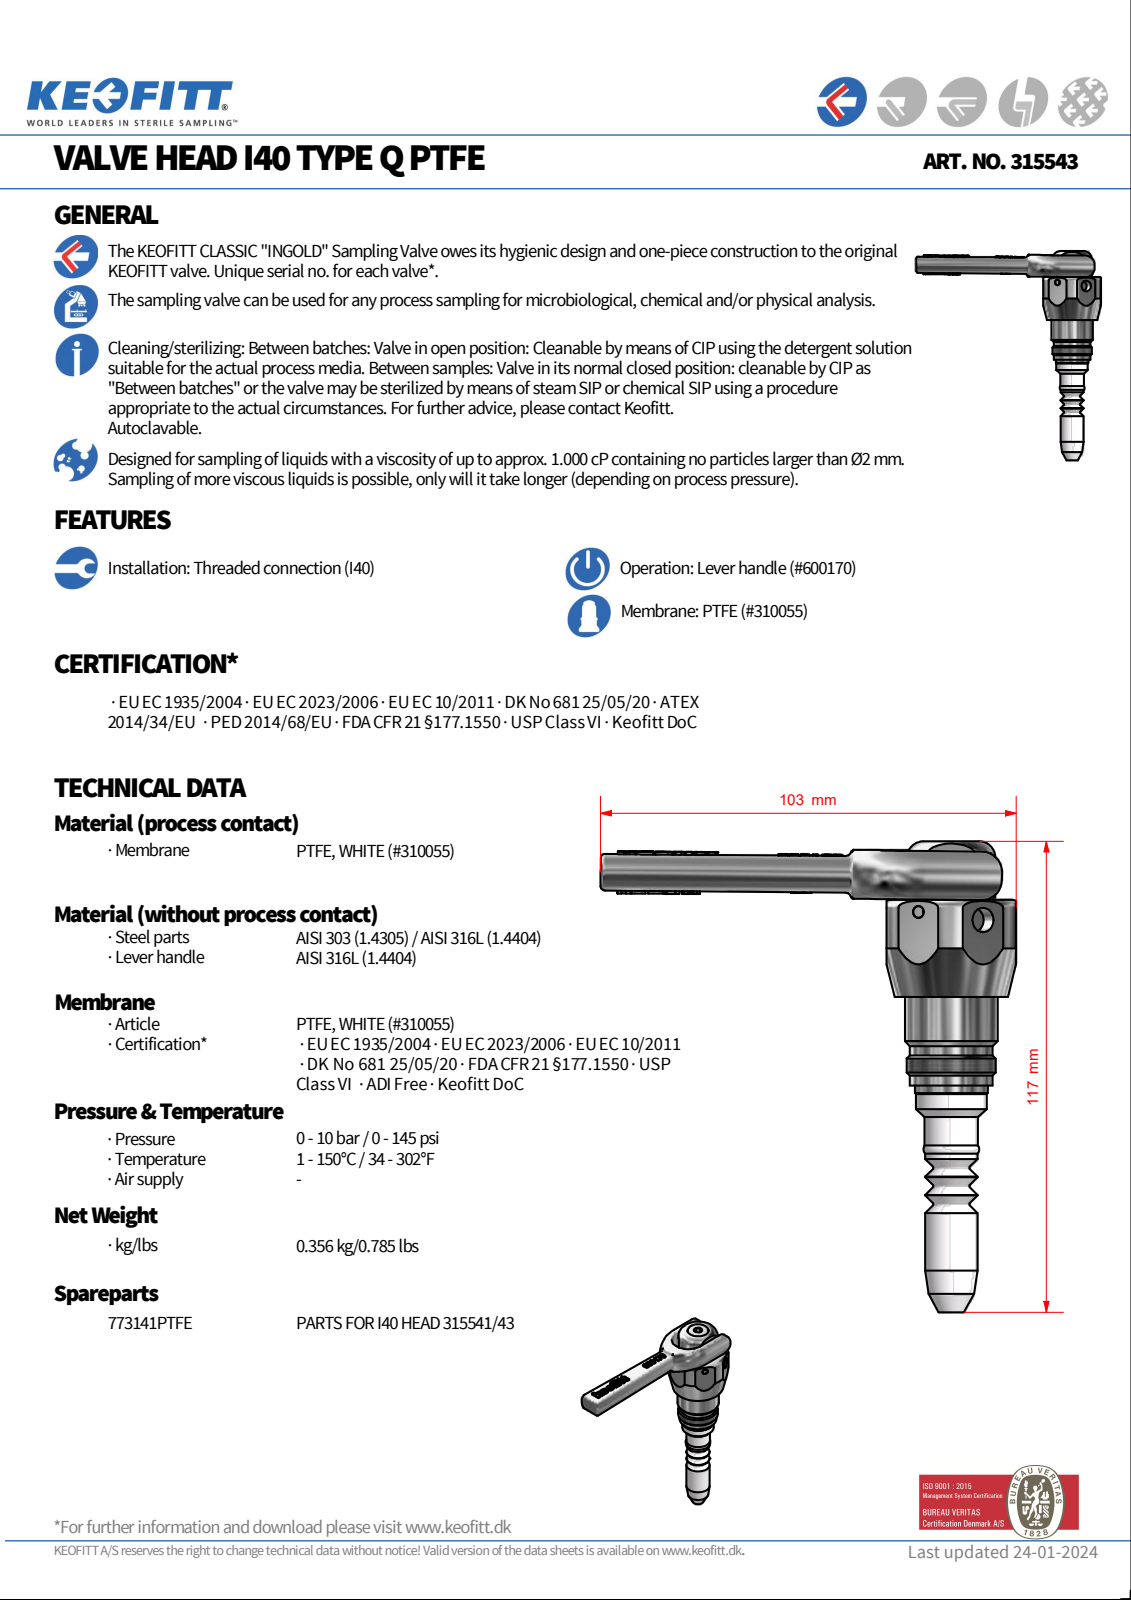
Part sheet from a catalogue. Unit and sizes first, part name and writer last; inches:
Units: inches
Overall size (bounding box): 4.685 × 4.591 × 1.888
Round holes (diameter × count): ⌀0.236 ×1
Round bosses / shafts (diameter × count): ⌀0.906 ×1, ⌀0.866 ×1, ⌀0.807 ×1, ⌀0.709 ×1, ⌀0.689 ×1, ⌀0.52 ×1, ⌀0.508 ×1, ⌀0.394 ×1
Partial cylindrical surfaces — rounded edges, fillets, slot ends (radius × count): R0.02 ×14, R0.008 ×10, R0.039 ×2, R0.059 ×2, R0.197 ×2, R0.118 ×1, R0.358 ×1, R0.429 ×1
Main face-to-face distances: 0.059, 0.079, 0.413, 0.02, 0.354, 0.433, 0.492, 0.472, 0.945, 0.965
Volume: 3.208 in³ · Surface area: 24.5 in²
Bodies: 2 solids, 494 faces (208 planar, 66 cylindrical, 220 other)
Part name (STEP PRODUCT): 315543
STEP written by: Autodesk Inventor 2022 (AUTOMOTIVE_DESIGN)
